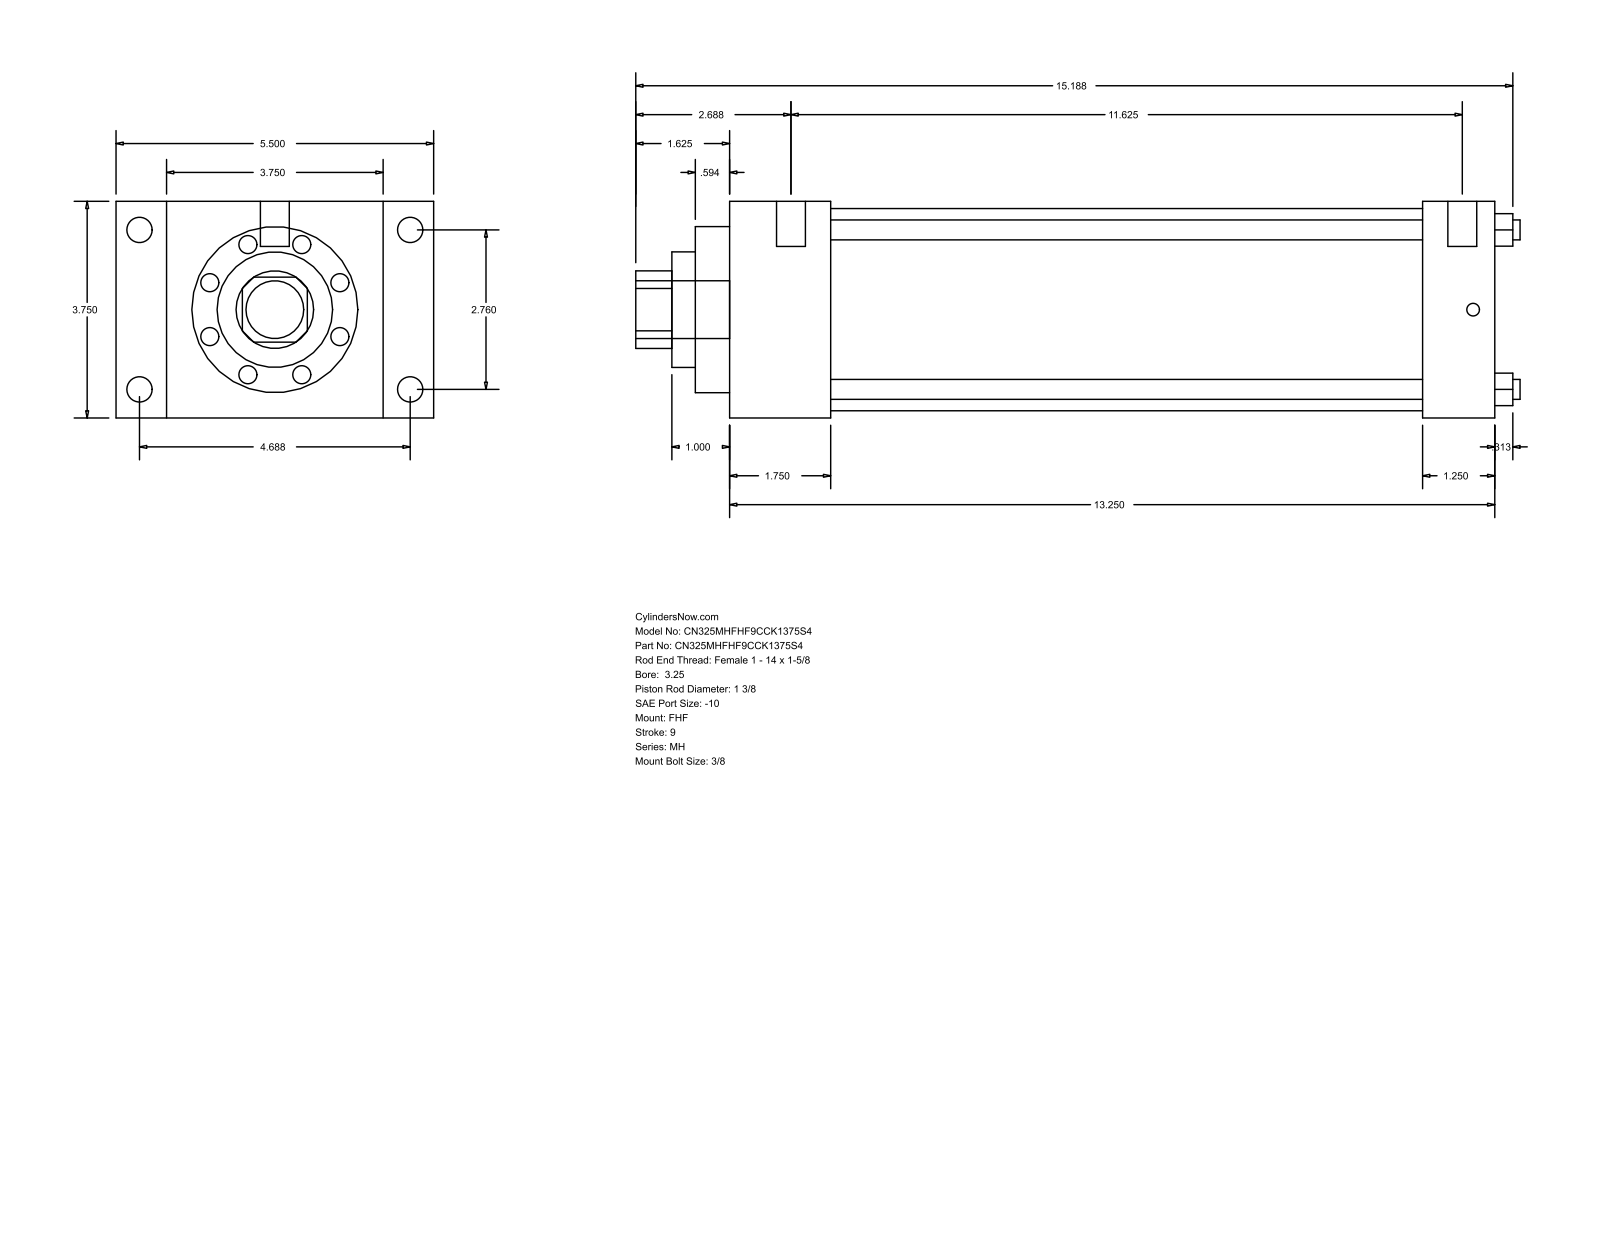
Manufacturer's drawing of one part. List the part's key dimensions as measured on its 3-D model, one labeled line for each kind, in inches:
Part name (STEP PRODUCT): MH_FHF__0325_1.375
STEP written by: GSSL Pune (CONFIG_CONTROL_DESIGN)
Units: inches
Bodies: 0 solids, 90 faces (61 planar, 29 cylindrical, 0 other)
Overall size (bounding box): 15.313 × 5.5 × 3.75
Round holes (diameter × count): ⌀0.345 ×4, ⌀1.375 ×1, ⌀2 ×1, ⌀2.875 ×1, ⌀3.5 ×1
Round bosses / shafts (diameter × count): ⌀0.438 ×4, ⌀0.219 ×4, ⌀0.5 ×2, ⌀1 ×1
Partial cylindrical surfaces — rounded edges, fillets, slot ends (radius × count): R0.672 ×1
Main face-to-face distances: 3.75, 13.25, 1.75, 11.5, 0.875, 4.625, 5.5, 12, 10.25, 1.25
Hole centre spacings: 1.952, 2.76, 3.903
